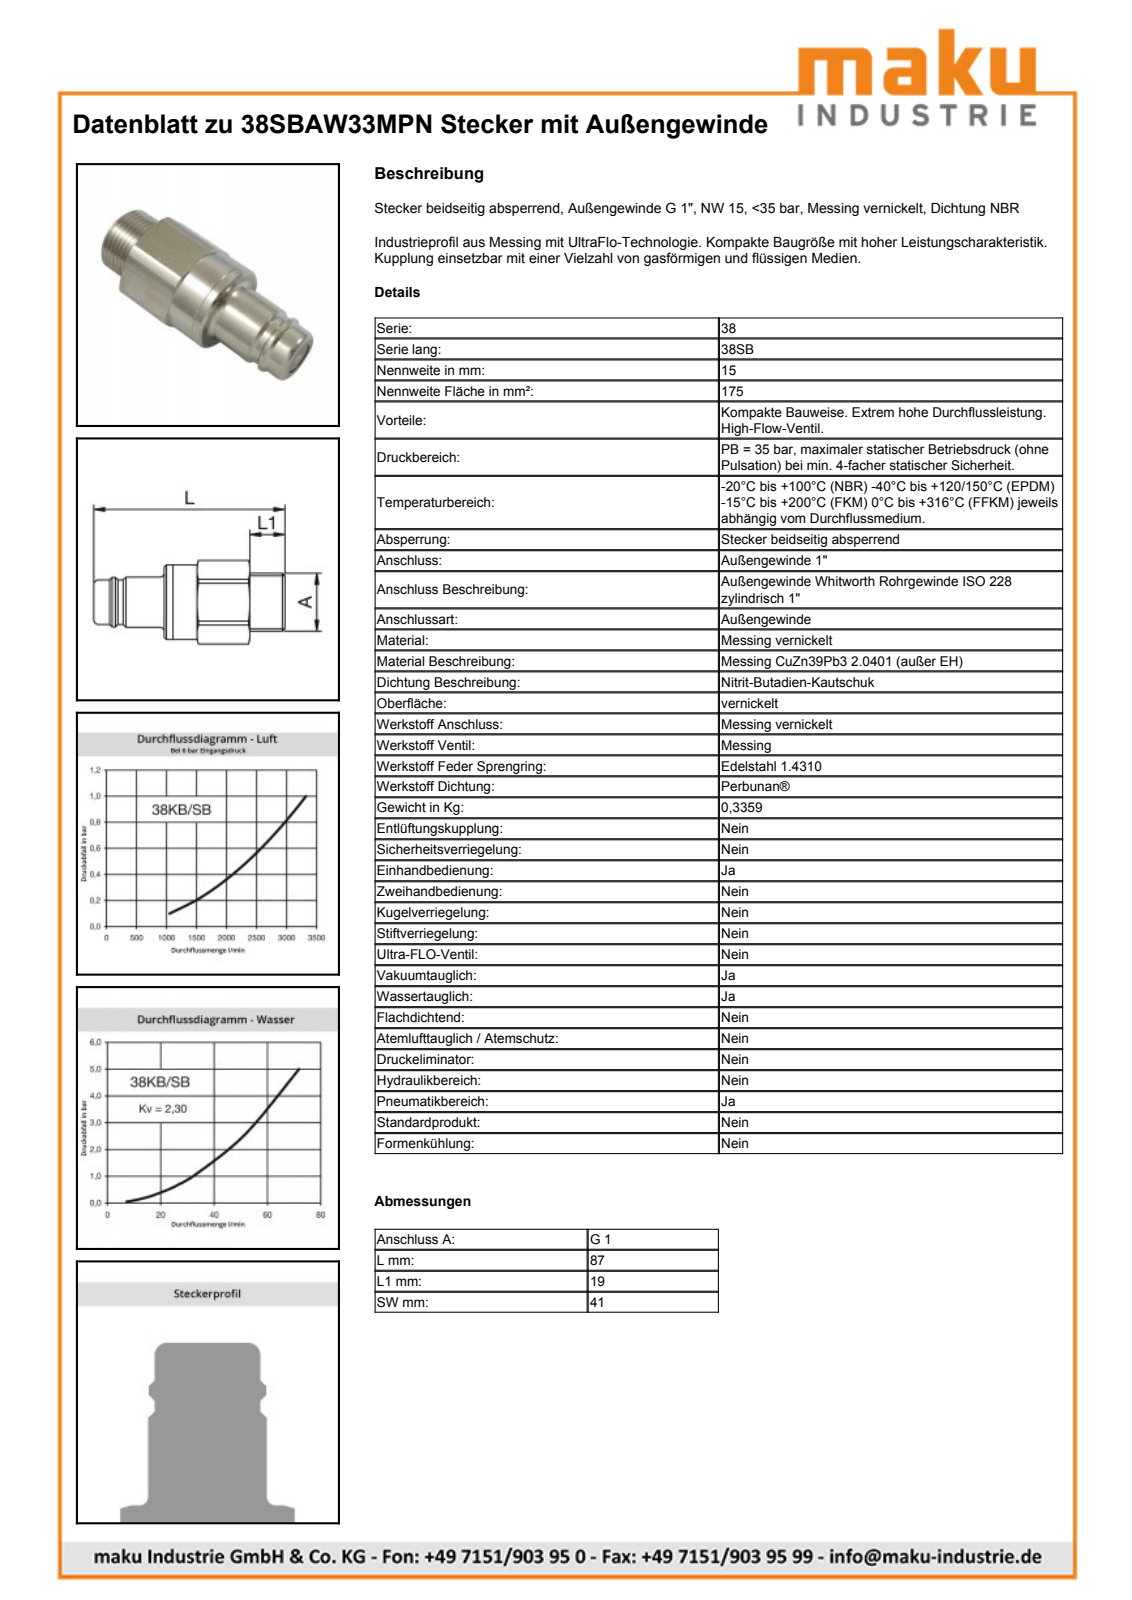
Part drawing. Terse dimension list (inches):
name: D111279
written by: Autodesk Inventor 2013 (AUTOMOTIVE_DESIGN)
unit: in
bodies: 1 solid, 62 faces (17 planar, 20 cylindrical, 25 other)
size: 3.425 × 1.772 × 1.68
volume: 4.363 in³; area: 20.43 in²
holes: 1× ⌀0.76, 1× ⌀1.14
bosses: 1× ⌀1.339, 1× ⌀1.309, 1× ⌀1.122, 1× ⌀1.01, 1× ⌀0.9, 1× ⌀0.89, 1× ⌀0.799, 1× ⌀0.745
rounds: 1× R0.886
face distances: 0.748, 0.827, 1.575, 1.614, 1.615, 1.613, 0.587, 1.413, 2.161, 1.264
